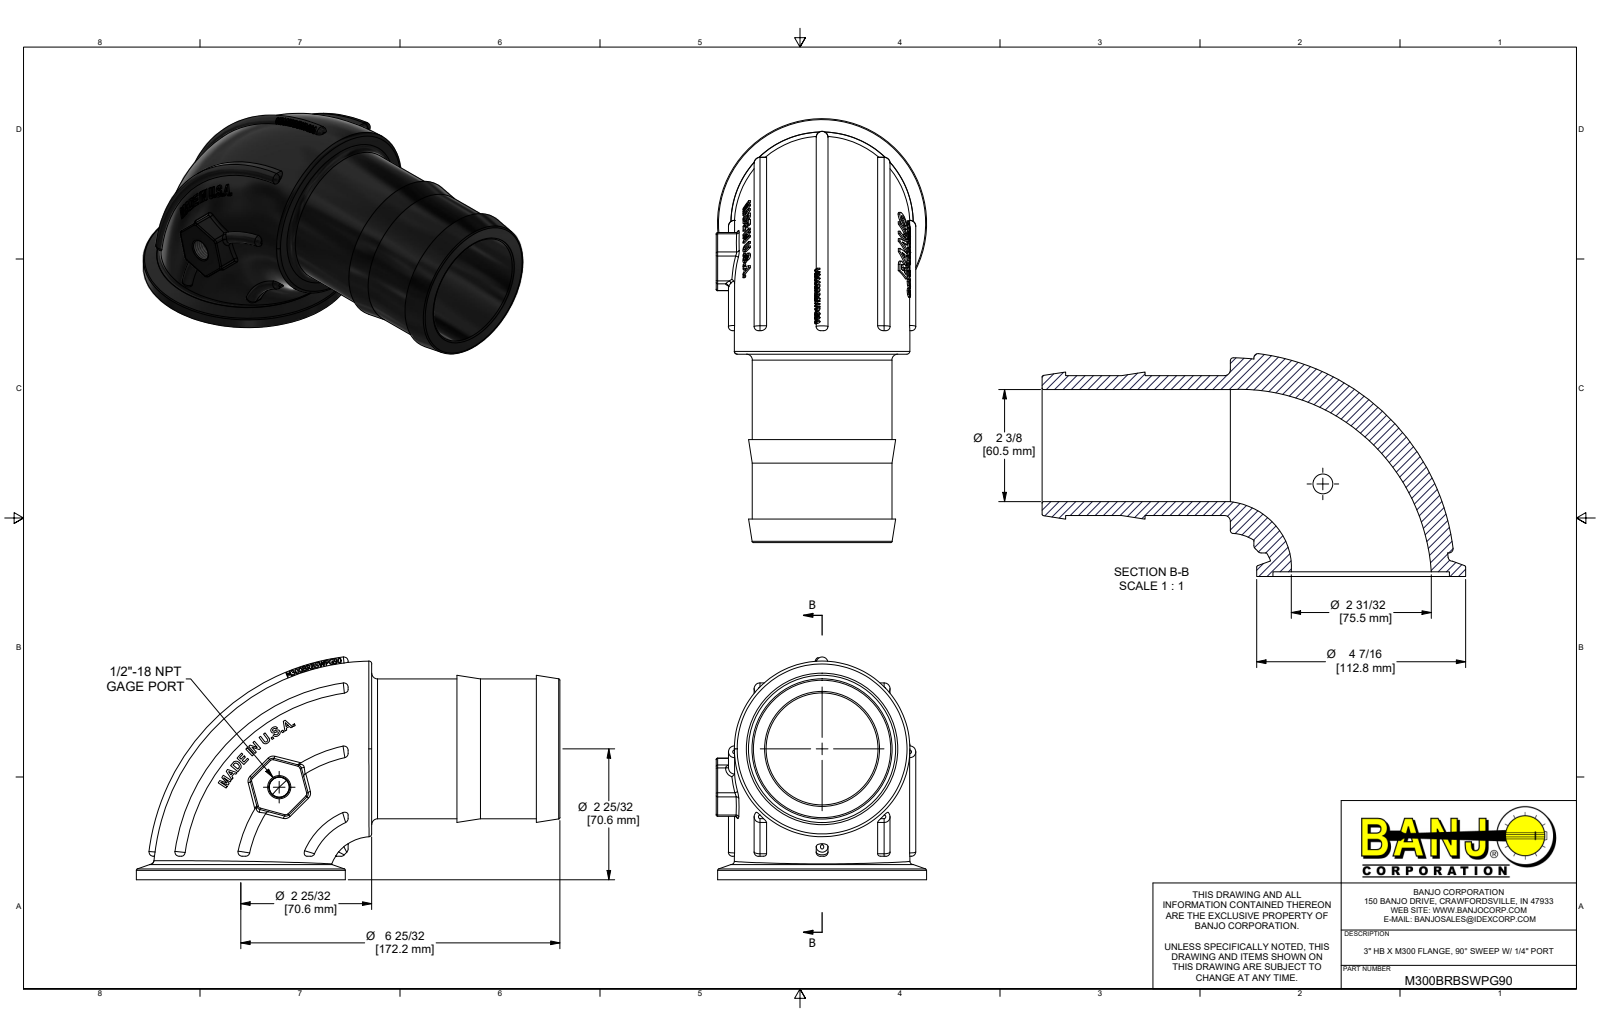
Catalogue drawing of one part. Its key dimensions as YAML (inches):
part_name: "M300BRBSWPG90; M300BRBSWPG90X"
step_written_by: "Autodesk Inventor 2019 (AUTOMOTIVE_DESIGN)"
units: inches
bodies: {solids: 1, faces: 729, planar: 309, cylindrical: 30, other: 390}
overall_size: [9, 4.733, 4.47]
volume: 35.03
surface_area: 182.4
round_holes:
  - {diameter: 0.422, count: 1}
  - {diameter: 2.38, count: 1}
  - {diameter: 3.75, count: 1}
round_bosses_or_shafts:
  - {diameter: 4.44, count: 1}
  - {diameter: 2.969, count: 1}
partial_cylinders:
  - {radius: 0.09, count: 10}
  - {radius: 0.03, count: 6}
  - {radius: 1.336, count: 1}
  - {radius: 4.224, count: 1}
face_to_face_distances: [0.1, 4, 0.5, 2.187, 1.687, 3.5, 1.813, 1.125, 1.125, 0.324]
